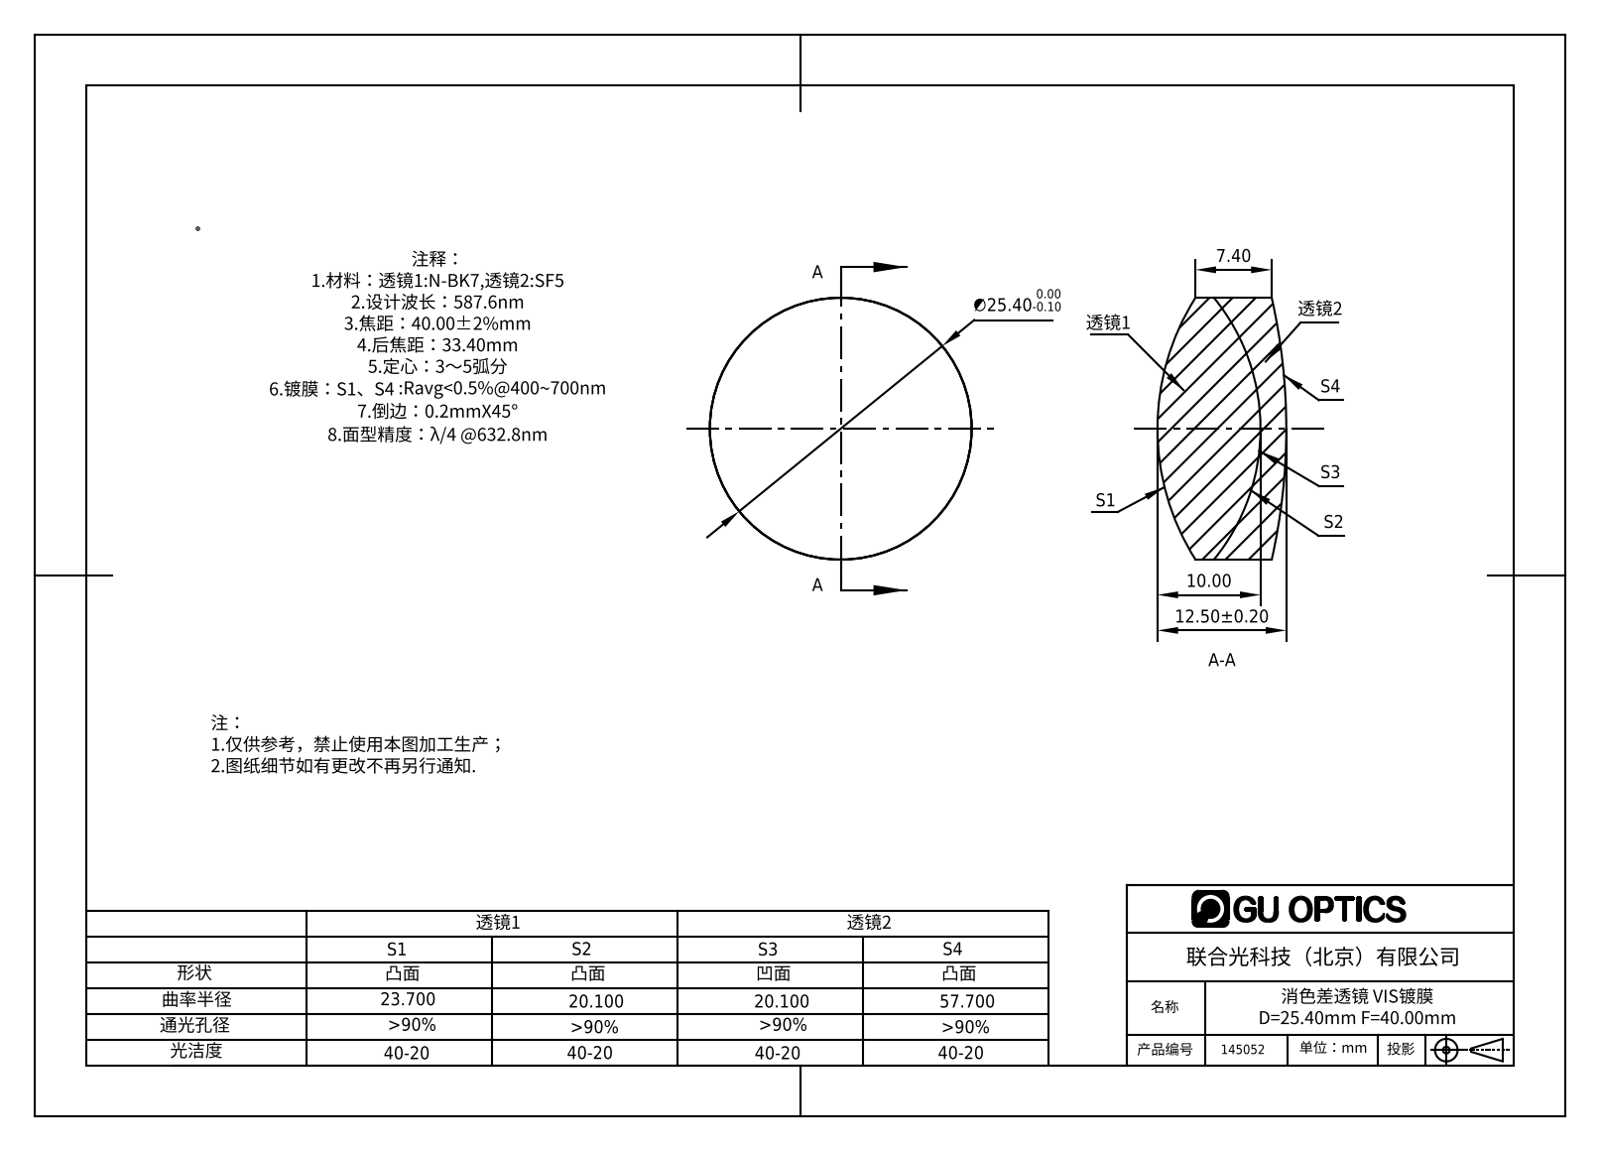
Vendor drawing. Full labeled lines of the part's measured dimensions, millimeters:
Part name (STEP PRODUCT): 145052
STEP written by: SolidWorks 2016 (AUTOMOTIVE_DESIGN)
Units: millimetres
Bodies: 2 solids, 12 faces (0 planar, 4 cylindrical, 8 other)
Overall size (bounding box): 25.4 × 25.4 × 12.5
Volume: 5 068 mm³ · Surface area: 2 794 mm²
Round bosses / shafts (diameter × count): ⌀25.4 ×1
